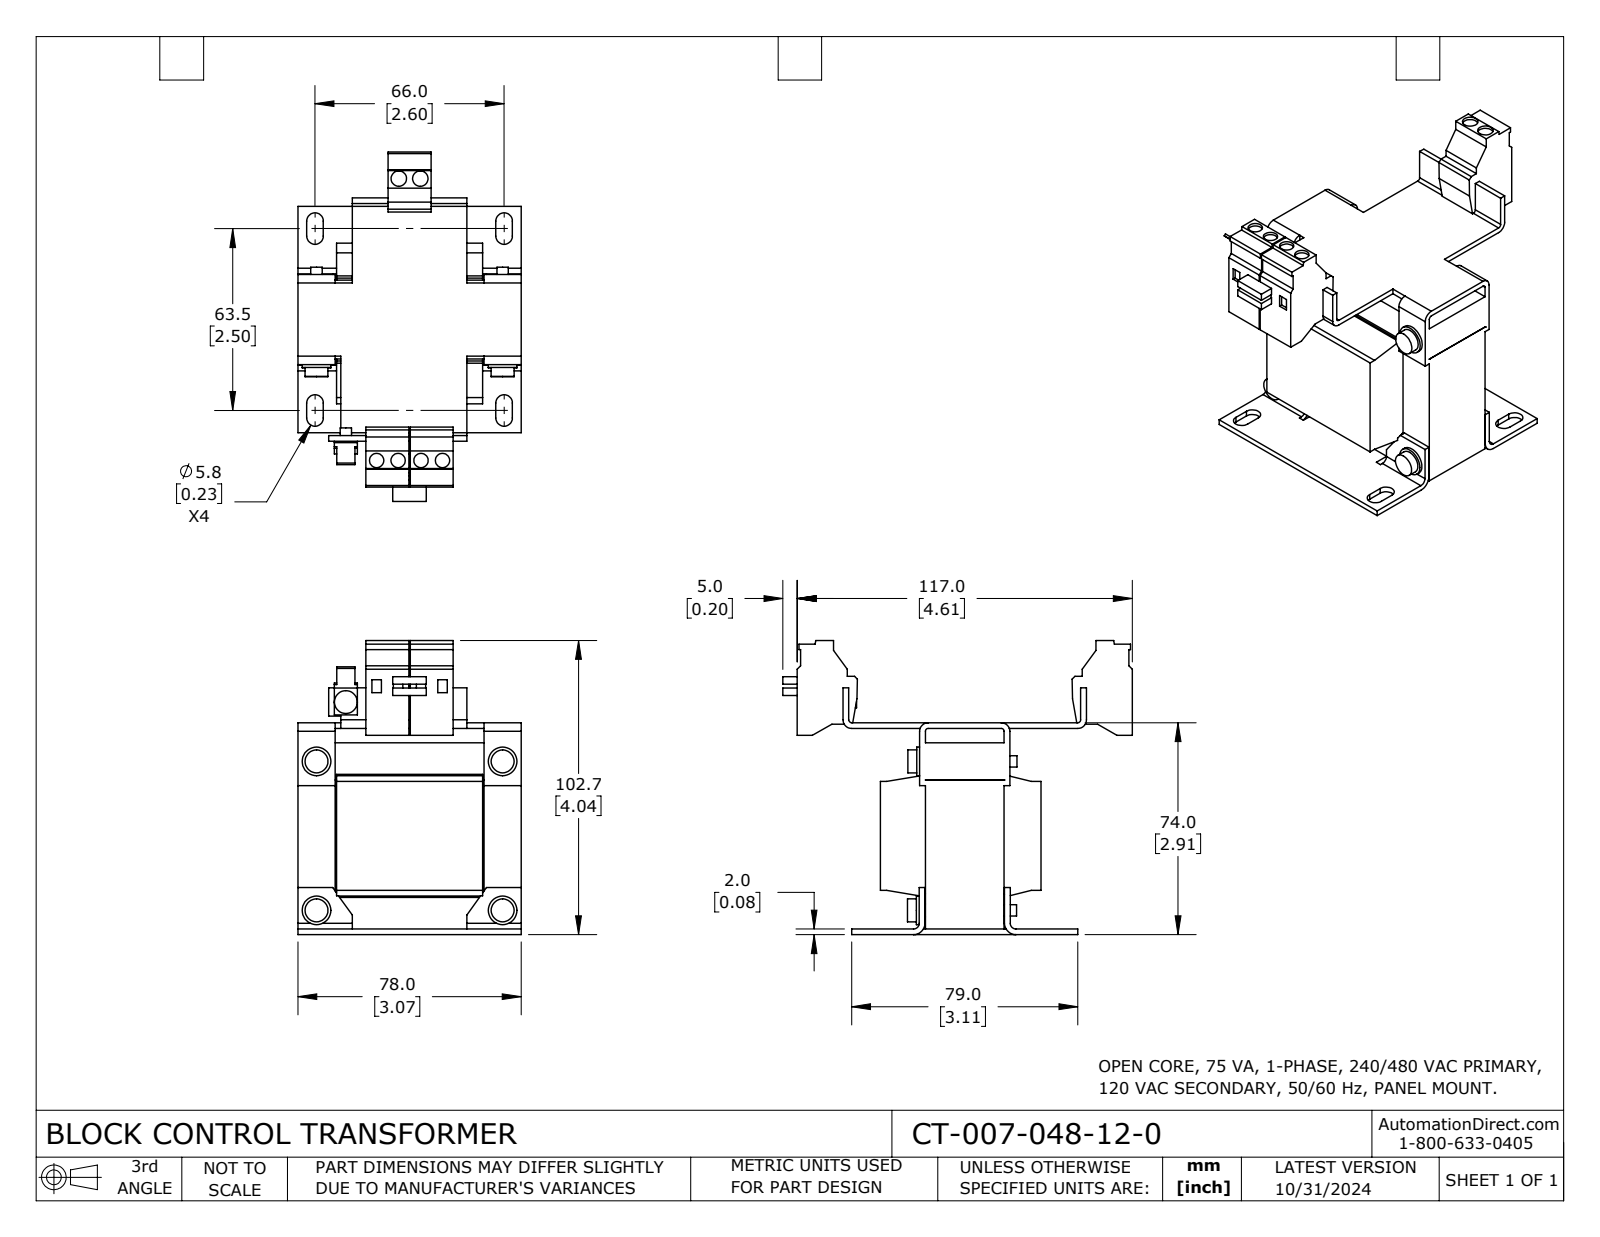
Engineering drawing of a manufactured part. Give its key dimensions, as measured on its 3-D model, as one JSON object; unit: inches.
{"part_name": "CT-007-048-12-0", "step_written_by": "SolidWorks 2023 (CONFIG_CONTROL_DESIGN)", "units": "inches", "bodies": {"solids": 1, "faces": 375, "planar": 294, "cylindrical": 81, "other": 0}, "overall_size": [4.803, 4.043, 3.071], "volume_in3": 14.96, "surface_area_in2": 99.05, "round_holes": [[0.197, 4], [0.213, 2]], "round_bosses_or_shafts": [[0.315, 5], [0.157, 5], [0.394, 4], [0.177, 2]], "partial_cylinders_radius": [[0.114, 8], [0.039, 4], [0.118, 4], [0.079, 2], [0.157, 2]], "face_to_face_distances": [0.079, 2.835, 0.531, 2.047, 0.512, 0.709, 0.02, 2.559, 2.028, 2.756], "hole_center_spacings": [3.886, 0.295, 0.61, 3.874, 3.92, 0.315, 0.906]}
